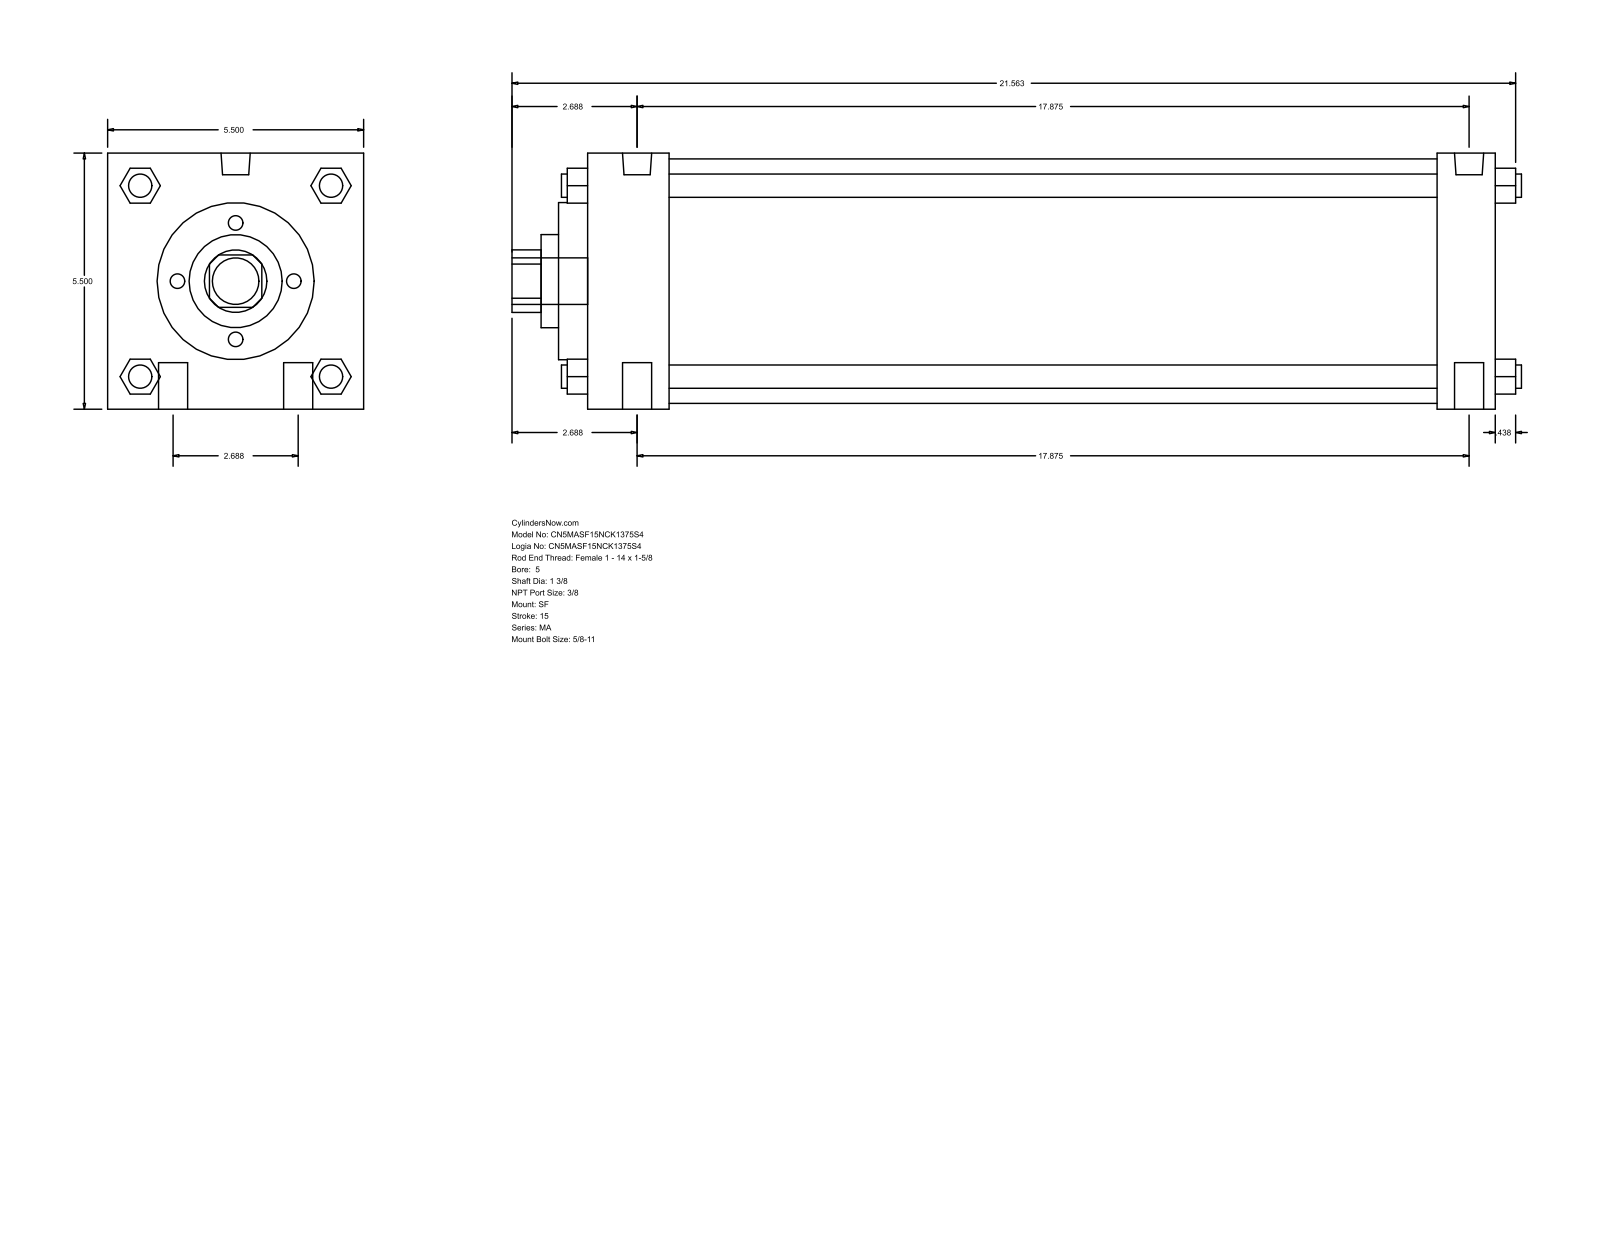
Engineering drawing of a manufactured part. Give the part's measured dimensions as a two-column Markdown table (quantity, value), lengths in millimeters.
| quantity | value |
| --- | --- |
| part name | MA_SF__0500_1.375 |
| STEP written by | GSSL Pune (CONFIG_CONTROL_DESIGN) |
| units | millimeters |
| bodies | 0 solids, 126 faces (95 planar, 31 cylindrical, 0 other) |
| overall size | 550.86 × 139.7 × 139.7 |
| round holes (diameter × count) | 34.92 × 1, 50.8 × 1, 85.72 × 1, 133.35 × 1 |
| round bosses / shafts (diameter × count) | 15.88 × 4, 12.7 × 4, 15.93 × 2, 11.11 × 2, 25.4 × 1 |
| partial cylindrical surfaces (radius × count) | 17.06 × 1 |
| main face-to-face distances | 139.7, 495.31, 44.45, 463.55, 419.1, 450.86, 31.76, 15.87, 60.32, 479.42 |
